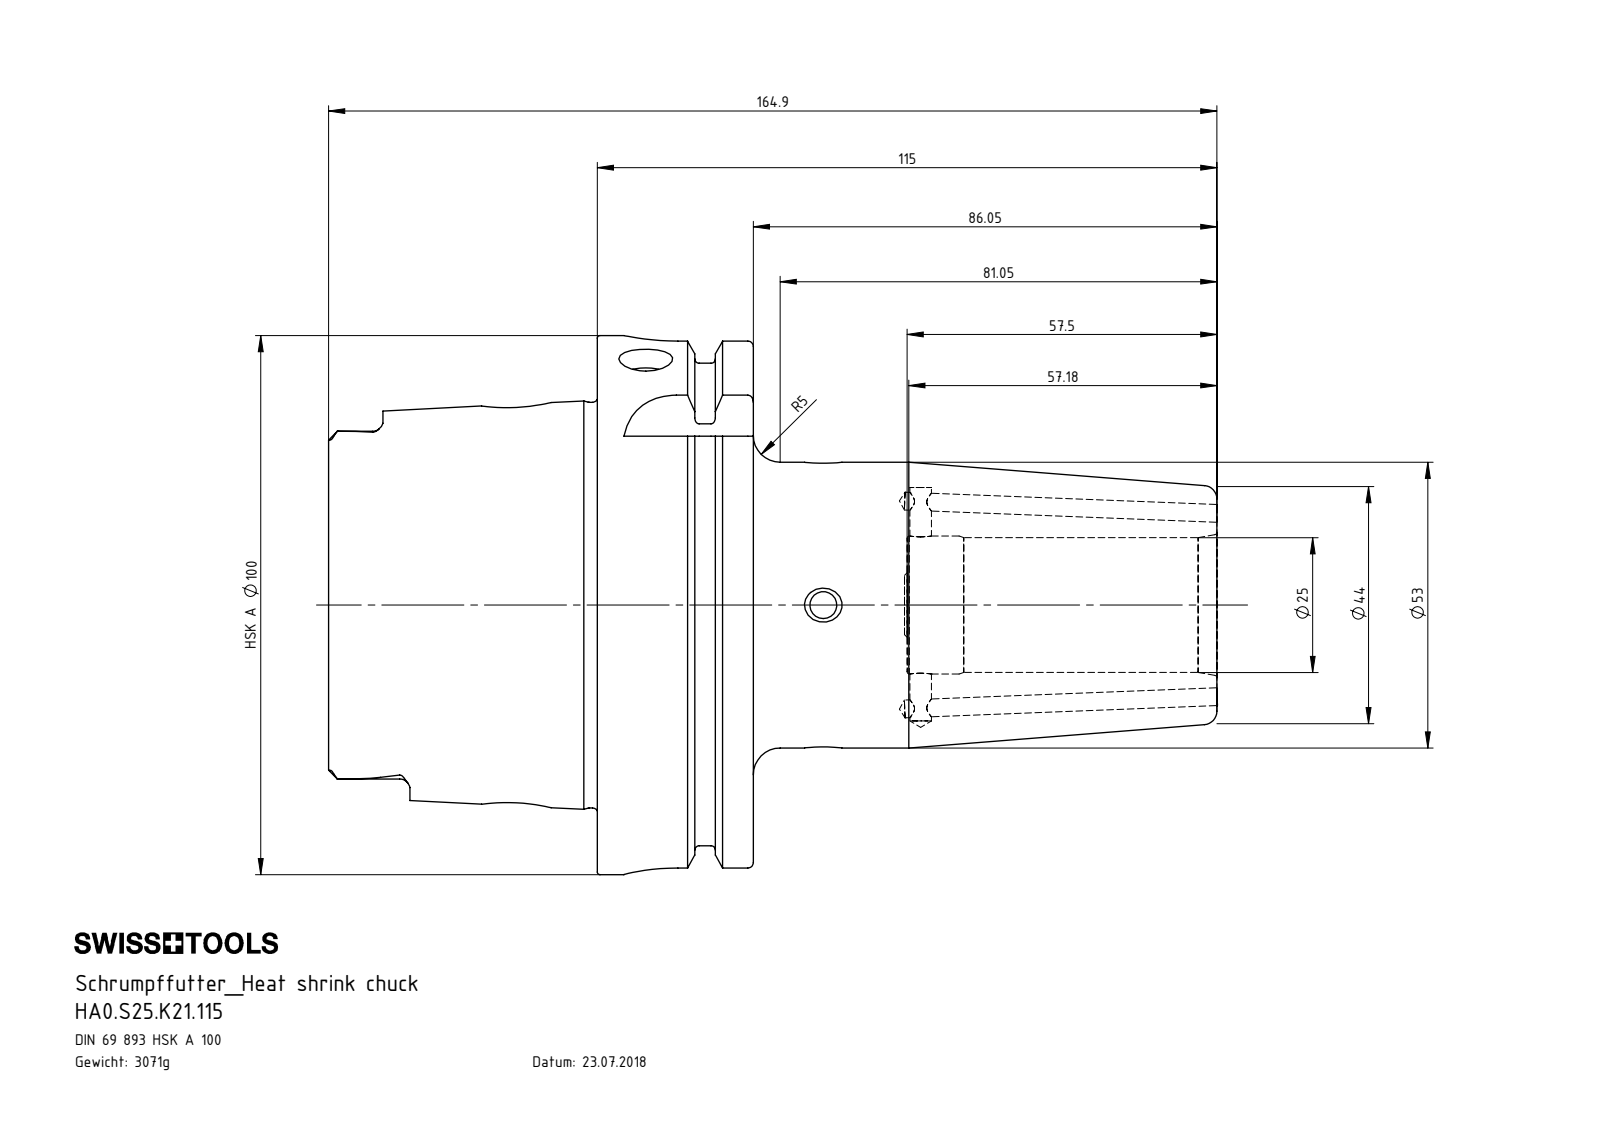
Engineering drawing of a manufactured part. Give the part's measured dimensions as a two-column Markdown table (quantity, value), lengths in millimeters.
| quantity | value |
| --- | --- |
| part name | ERU-AN5.K01.020_A; HA0-S25.K21.115_C_Fertigbearbeitung; HA0.S25.K21.115; ERU-CJ3.001.008 |
| STEP written by | SolidWorks 2017 (CONFIG_CONTROL_DESIGN) |
| units | millimeters |
| bodies | 4 solids, 299 faces (95 planar, 86 cylindrical, 118 other) |
| overall size | 165 × 100 × 100 |
| volume | 391 227 mm³ |
| surface area | 71 325 mm² |
| round holes (diameter × count) | 10 × 3, 3.3 × 2, 5 × 2, 12 × 2, 4 × 1, 6 × 1, 11 × 1, 22.5 × 1, 25 × 1, 25.6 × 1, 26 × 1, 53 × 1 |
| round bosses / shafts (diameter × count) | 4 × 2, 100 × 1, 91.95 × 1, 75.26 × 1 |
| partial cylindrical surfaces (radius × count) | 1.9 × 6, 4.88 × 4, 10 × 4 |
| main face-to-face distances | 28.95, 12.45, 16.5, 49.9, 62.35, 78.85, 57.5, 164.9, 115, 102.55 |
| hole center spacings | 18.05, 34.95, 56.95, 75 |
